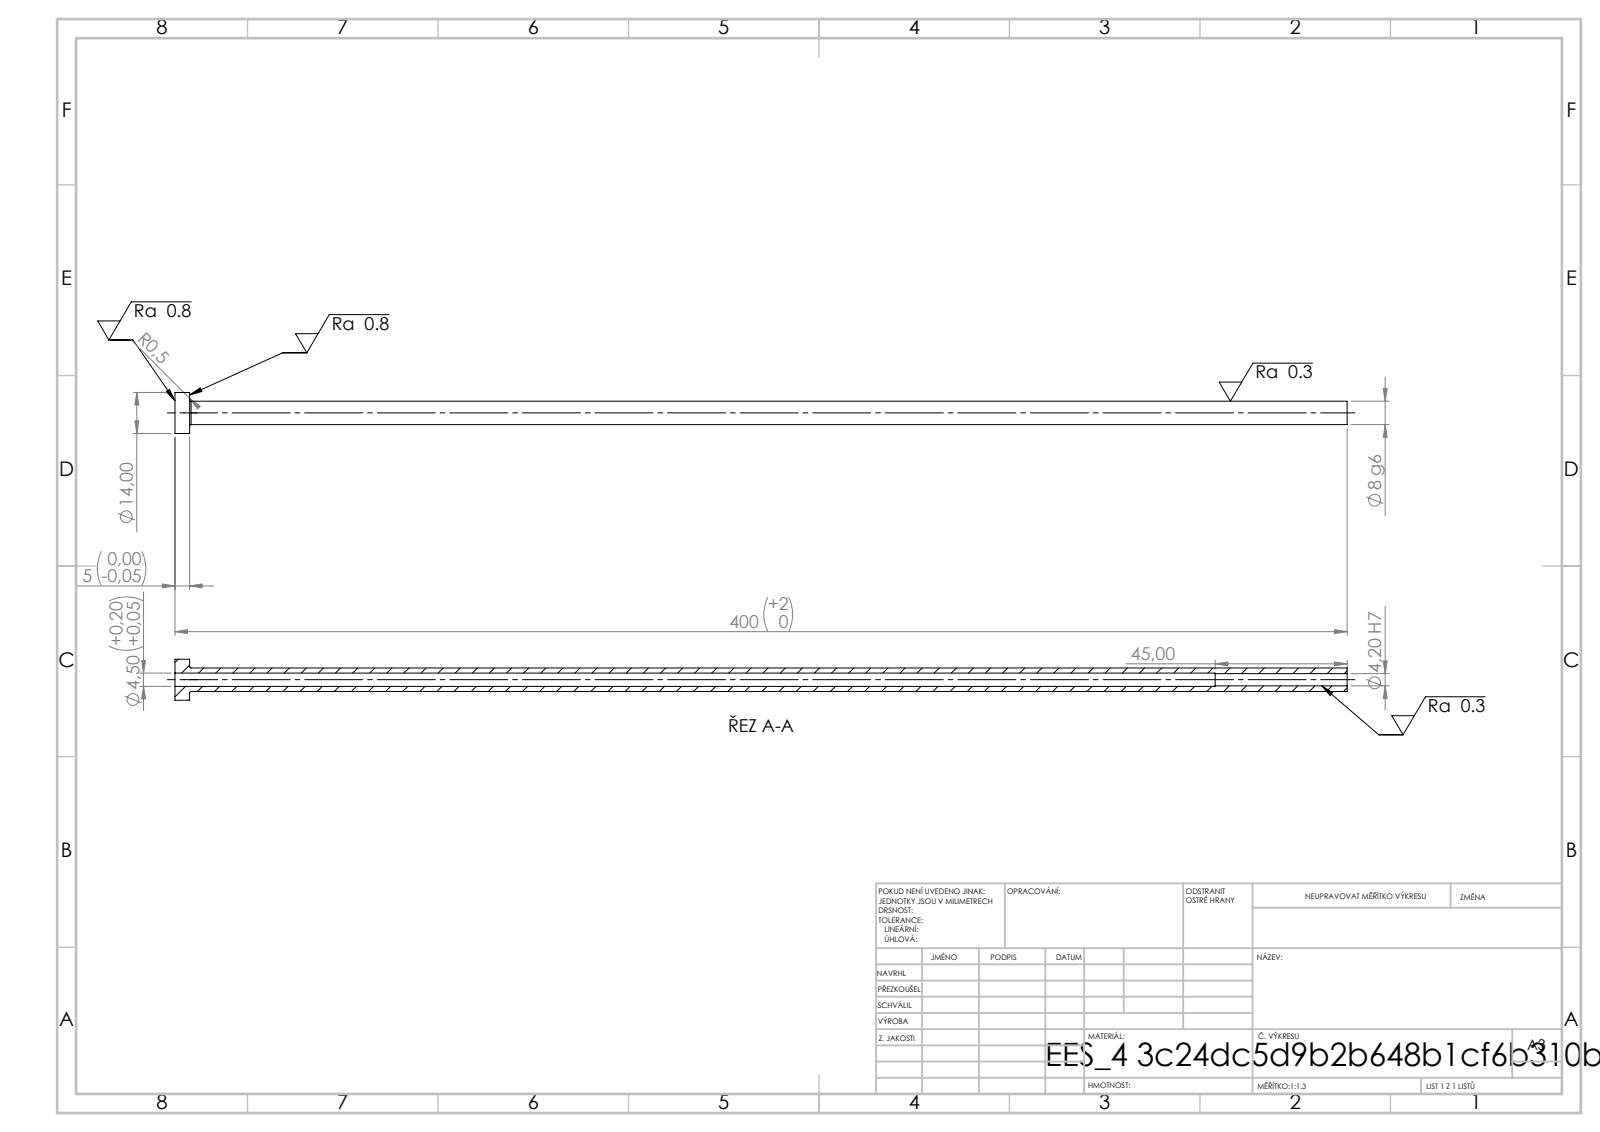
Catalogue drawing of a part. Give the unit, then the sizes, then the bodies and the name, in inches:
Units: inches
Overall size (bounding box): 15.748 × 0.551 × 0.551
Round holes (diameter × count): ⌀0.165 ×1, ⌀0.177 ×1
Round bosses / shafts (diameter × count): ⌀0.551 ×1, ⌀0.315 ×1
Main face-to-face distances: 0.197, 15.748, 15.551, 13.976, 13.78, 1.772
Volume: 0.876 in³ · Surface area: 24.85 in²
Bodies: 1 solid, 14 faces (4 planar, 8 cylindrical, 2 other)
STEP written by: SolidWorks 2019 (CONFIG_CONTROL_DESIGN)
